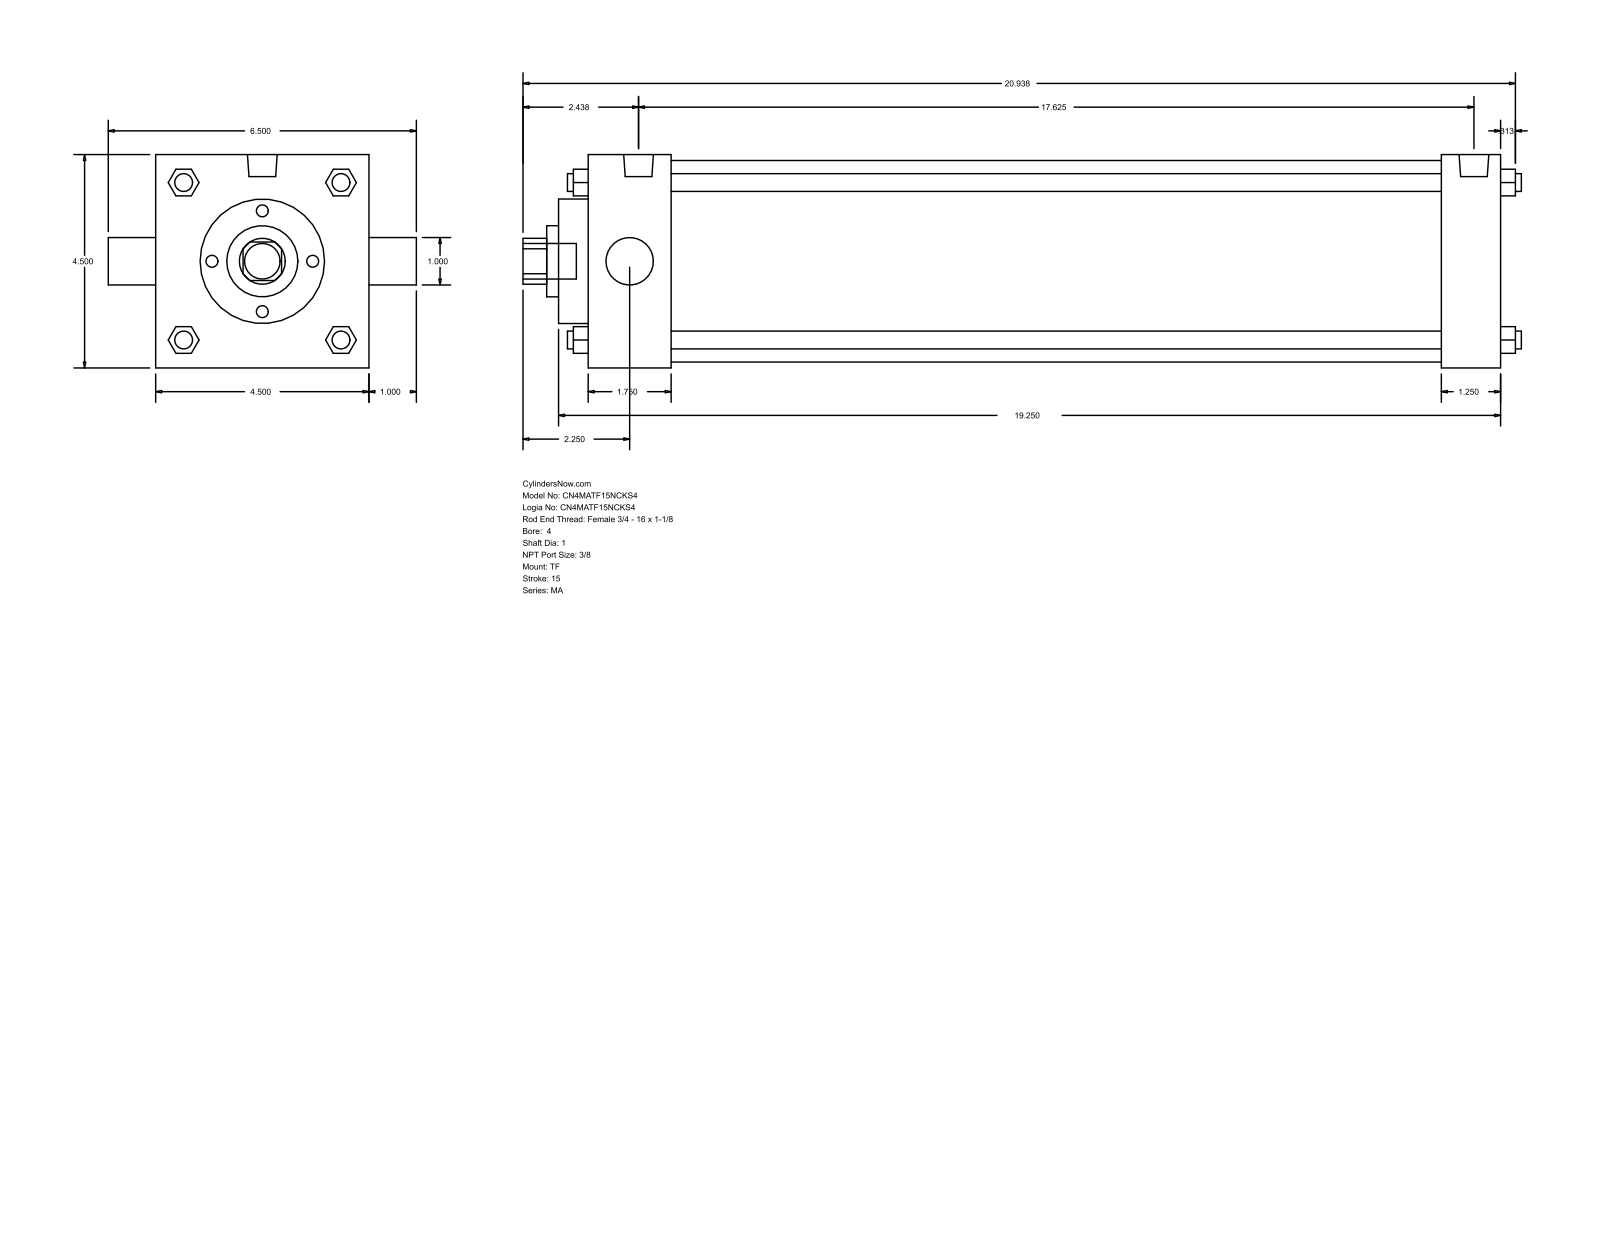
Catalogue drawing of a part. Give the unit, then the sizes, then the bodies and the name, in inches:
Units: inches
Overall size (bounding box): 21.063 × 6.5 × 4.5
Round holes (diameter × count): ⌀1 ×2, ⌀1.5 ×1, ⌀2.625 ×1, ⌀4.25 ×1
Round bosses / shafts (diameter × count): ⌀0.375 ×4, ⌀0.437 ×3, ⌀0.627 ×2, ⌀0.75 ×1
Partial cylindrical surfaces — rounded edges, fillets, slot ends (radius × count): R0.484 ×1
Main face-to-face distances: 4.5, 19.25, 18, 1.25, 1.75, 16.25, 17.5, 0.625, 2.375, 18.625
Bodies: 0 solids, 122 faces (93 planar, 29 cylindrical, 0 other)
Part name (STEP PRODUCT): MA_TF__0400_1
STEP written by: GSSL Pune (CONFIG_CONTROL_DESIGN)
